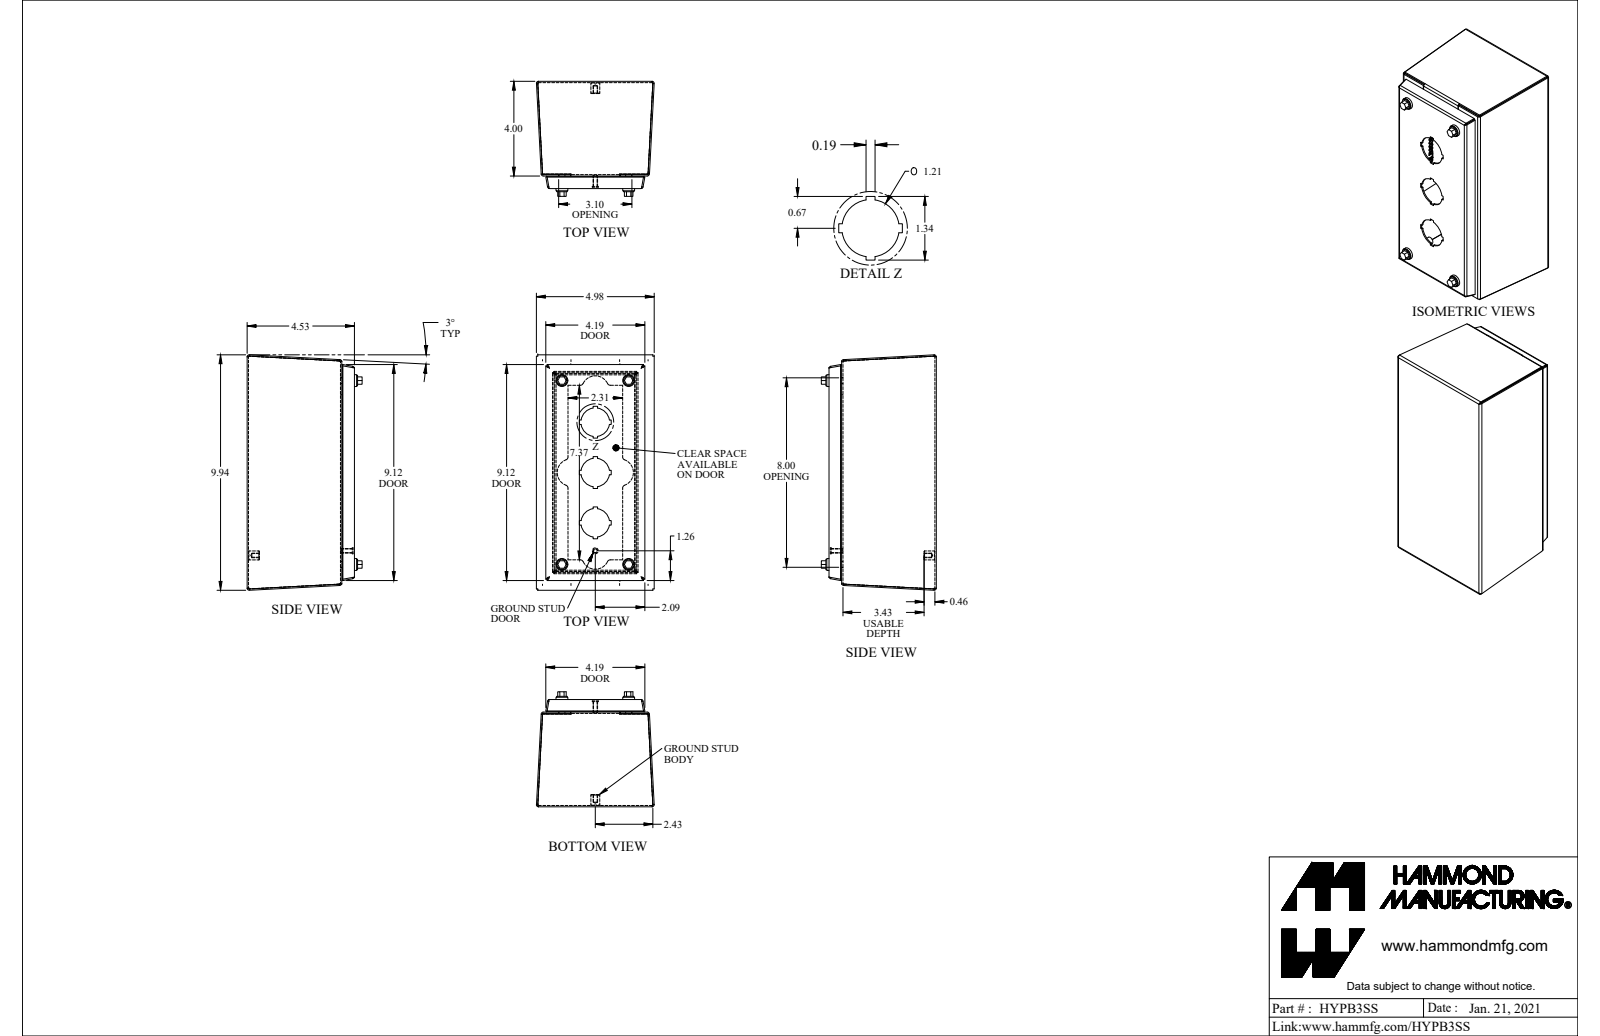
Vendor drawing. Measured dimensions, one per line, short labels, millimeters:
name: HYPB3SS
written by: SolidWorks 2021 (AUTOMOTIVE_DESIGN)
unit: mm
bodies: 22 solids, 491 faces (328 planar, 140 cylindrical, 23 other)
size: 252.5 × 126.4 × 123.4
volume: 286 800 mm³; area: 362 000 mm²
holes: 4× ⌀1.7, 4× ⌀6, 4× ⌀6.1, 4× ⌀6.1, 4× ⌀6.4, 4× ⌀6.4, 4× ⌀10.2, 3× ⌀30.7, 1× ⌀4
bosses: 5× ⌀9.5, 5× ⌀4.8, 4× ⌀12.7, 4× ⌀11.4, 4× ⌀10.3, 4× ⌀8, 1× ⌀6.4
rounds: 16× R0.7, 16× R2.2, 8× R3.2, 4× R1.4, 4× R1.9, 4× R12.7, 4× R14.6
face distances: 1.4, 112.2, 113.7, 100.2, 1.4, 115.1, 113.7, 12.1, 101.6, 13.5
hole spacings: 197.3, 209.9, 71.6, 197.3, 209.8, 104.9, 71.6, 57.2
